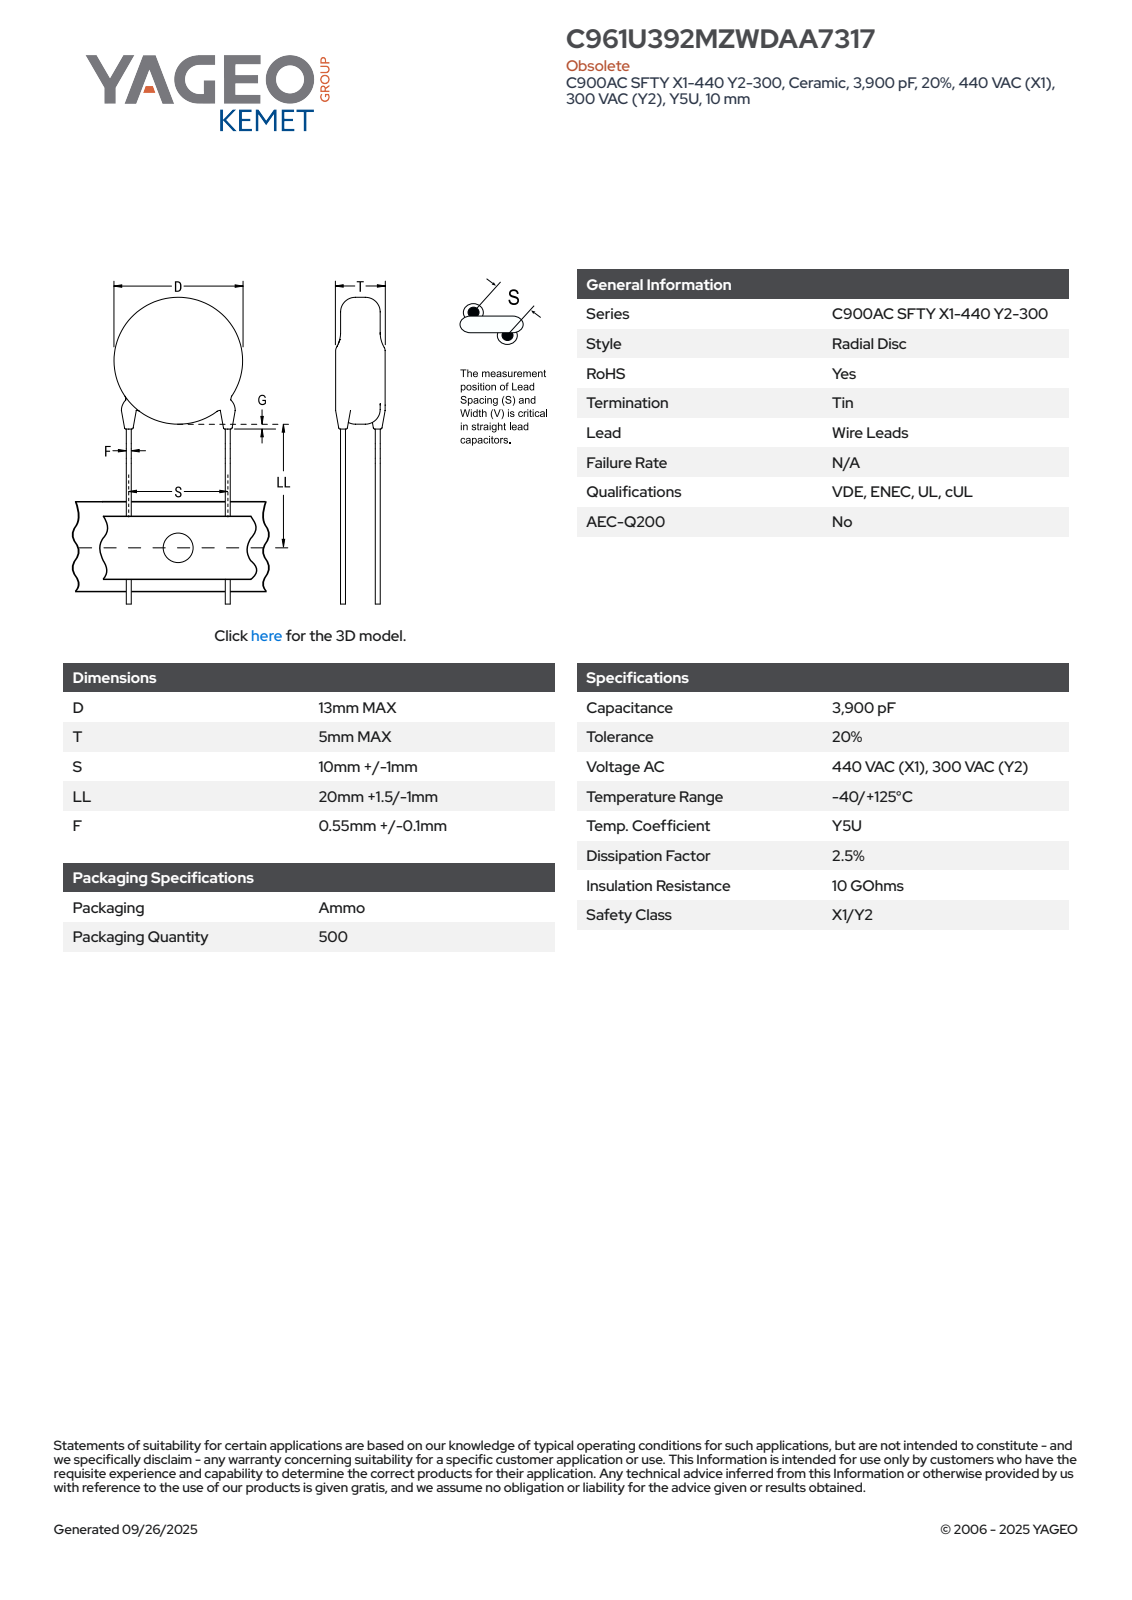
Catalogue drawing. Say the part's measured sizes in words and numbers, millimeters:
The part is named "CCD_STC900_D13T5S10LL21.5F0.65G3". Its 3-D file was written by "SolidWorks 2014 (AUTOMOTIVE_DESIGN)". It is 4 solids with 83 faces: 61 planar, 6 cylindrical and 16 other. Overall it measures 34.5 by 13 by 5 millimeters. Its volume is 664 cubic millimeters and its surface area 544 square millimeters. Round bosses or shafts: 2 of diameter 0.65, 1 of diameter 13. The main face-to-face distances are 5, 1.5, 28.75, 27.25, 0.41, 6.13, 0.93, 3.1, 4.45, 4.63.
